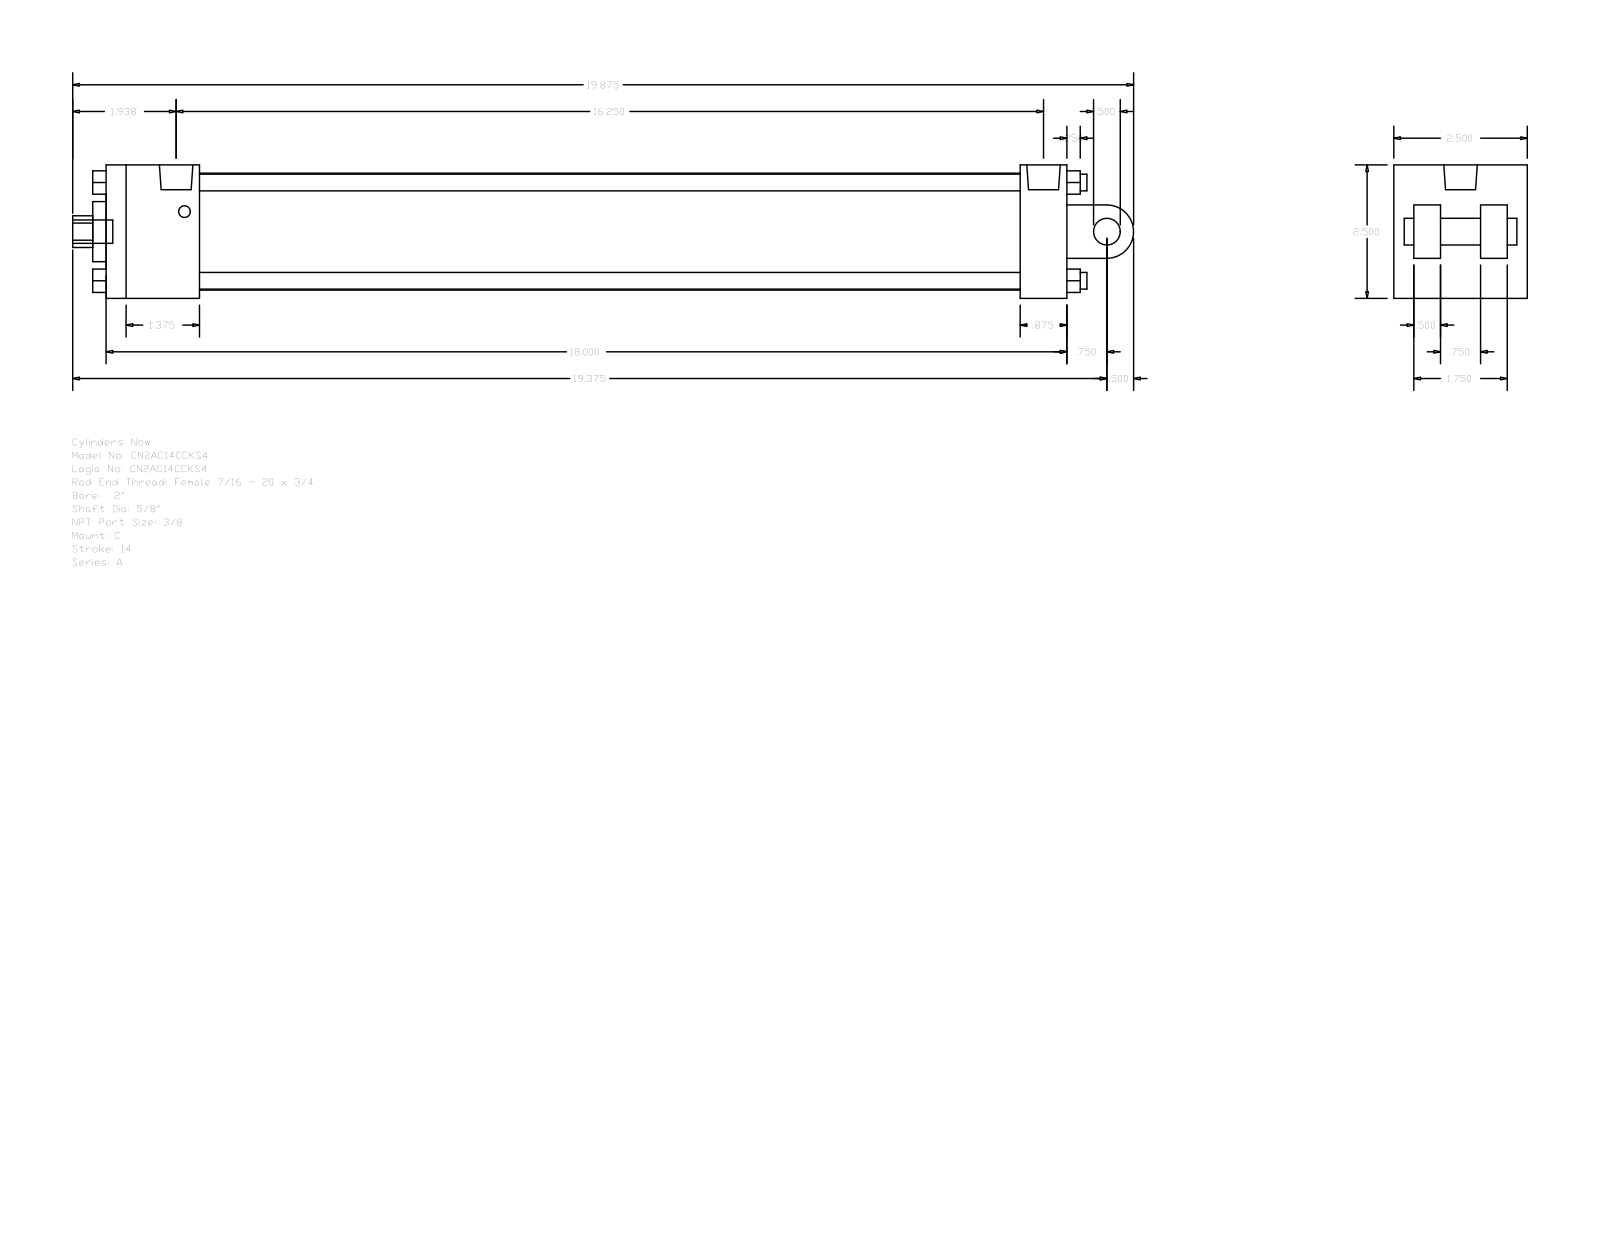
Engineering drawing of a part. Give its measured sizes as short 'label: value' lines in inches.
name: A_C__0200_0.625
written by: GSSL Pune (CONFIG_CONTROL_DESIGN)
unit: in
bodies: 0 solids, 135 faces (102 planar, 33 cylindrical, 0 other)
size: 19.875 × 2.5 × 2.5
holes: 2× ⌀0.219, 1× ⌀0.625, 1× ⌀0.627, 1× ⌀1.125, 1× ⌀2.19
bosses: 4× ⌀0.313, 2× ⌀0.219, 1× ⌀0.627, 1× ⌀0.5, 1× ⌀0.437
rounds: 1× R0.297, 1× R0.5
face distances: 2.5, 18, 0.875, 1.75, 16.25, 17.125, 15.375, 0.5, 1.625, 0.375
hole spacings: 0.156
